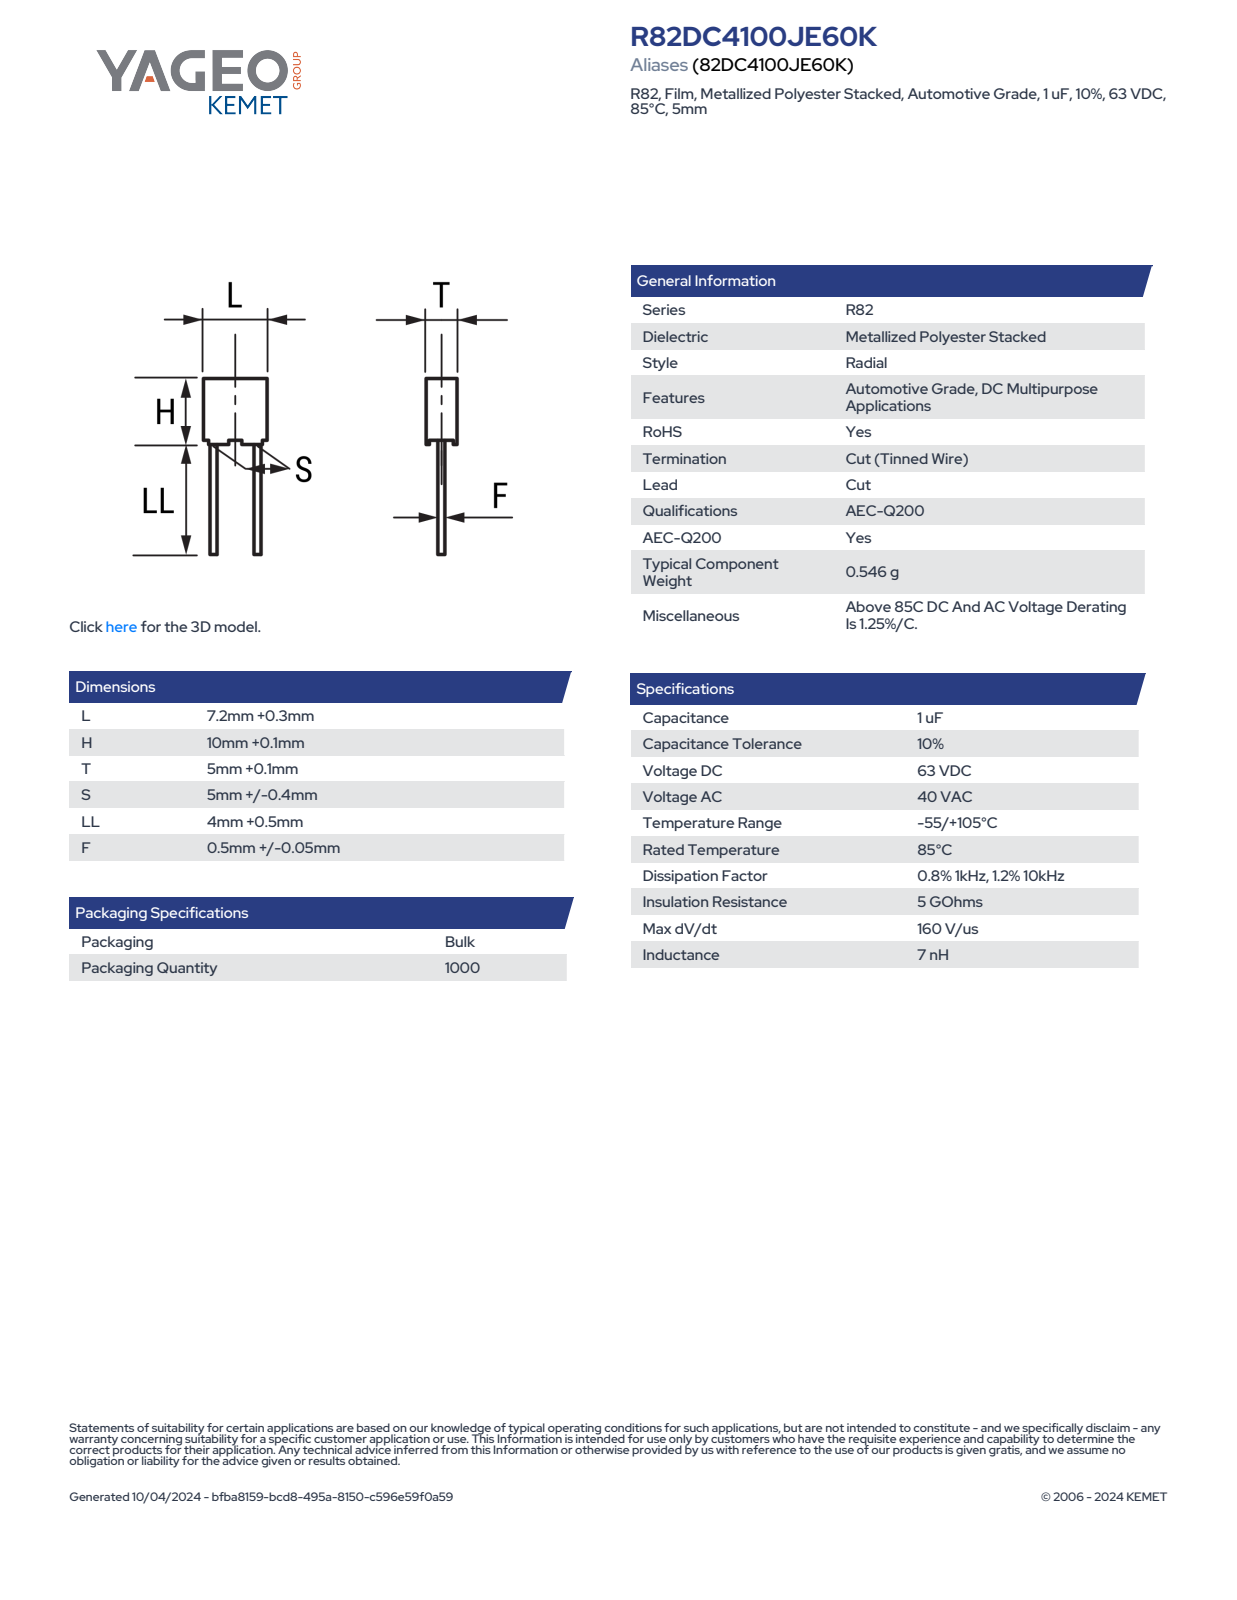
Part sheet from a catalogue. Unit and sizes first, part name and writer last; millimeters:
Units: millimetres
Overall size (bounding box): 14.6 × 7.5 × 5.11
Round bosses / shafts (diameter × count): ⌀0.55 ×2
Partial cylindrical surfaces — rounded edges, fillets, slot ends (radius × count): R0.5 ×4
Main face-to-face distances: 5.1, 7.5, 9.35, 4.85, 7.25, 0.75, 10.1, 4.6, 7, 0.35
Volume: 363 mm³ · Surface area: 363 mm²
Bodies: 4 solids, 85 faces (77 planar, 8 cylindrical, 0 other)
Part name (STEP PRODUCT): CFR_RB3_7.2X10X5_L7.5H10.1T5.1S5LL4.5F0.55
STEP written by: SolidWorks 2014 (AUTOMOTIVE_DESIGN)
